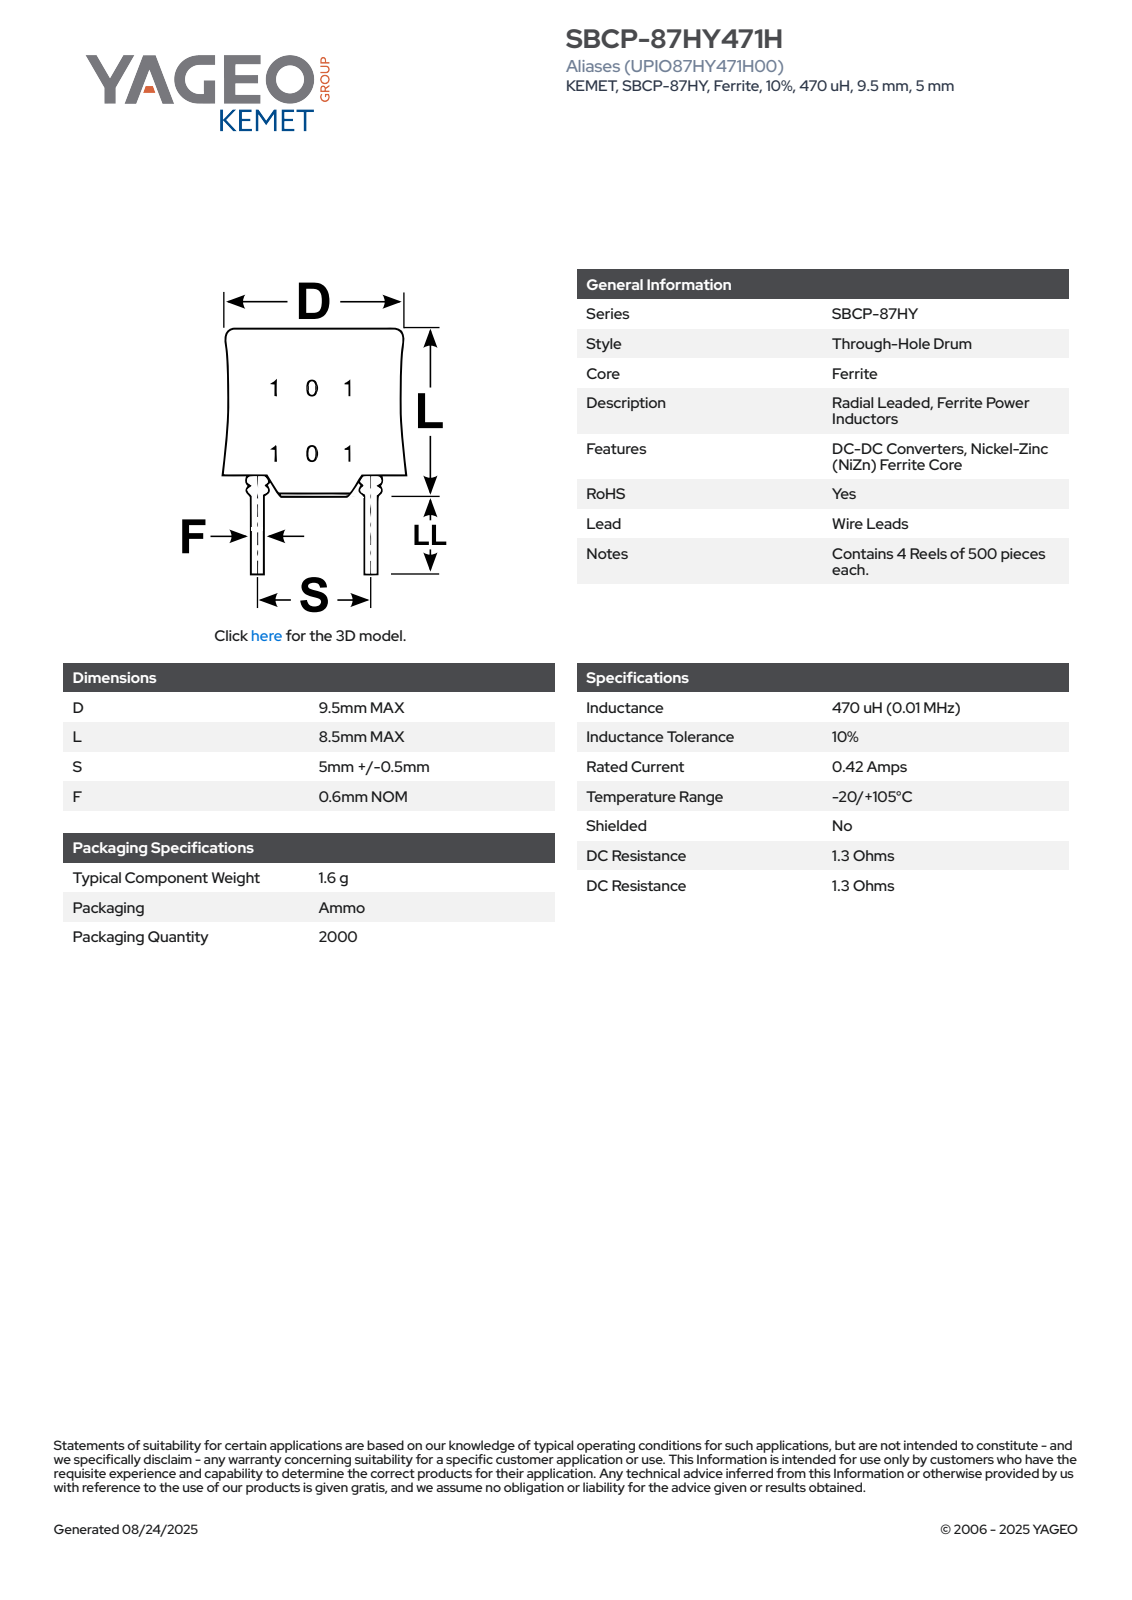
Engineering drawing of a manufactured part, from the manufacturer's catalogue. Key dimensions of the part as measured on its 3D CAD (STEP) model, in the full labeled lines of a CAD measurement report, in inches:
Part name (STEP PRODUCT): IL_SBCP87_D9.5L8.5S5LL4.5F0.6
STEP written by: SolidWorks 2014 (AUTOMOTIVE_DESIGN)
Units: inches
Bodies: 4 solids, 90 faces (69 planar, 13 cylindrical, 8 other)
Overall size (bounding box): 0.512 × 0.374 × 0.374
Volume: 0.027 in³ · Surface area: 0.673 in²
Round bosses / shafts (diameter × count): ⌀0.024 ×2, ⌀0.374 ×1, ⌀0.314 ×1
Partial cylindrical surfaces — rounded edges, fillets, slot ends (radius × count): R0.157 ×1
Main face-to-face distances: 0.294, 0.056, 0.239, 0.253, 0.197, 0.042, 0.04, 0.096, 0.293, 0.335
